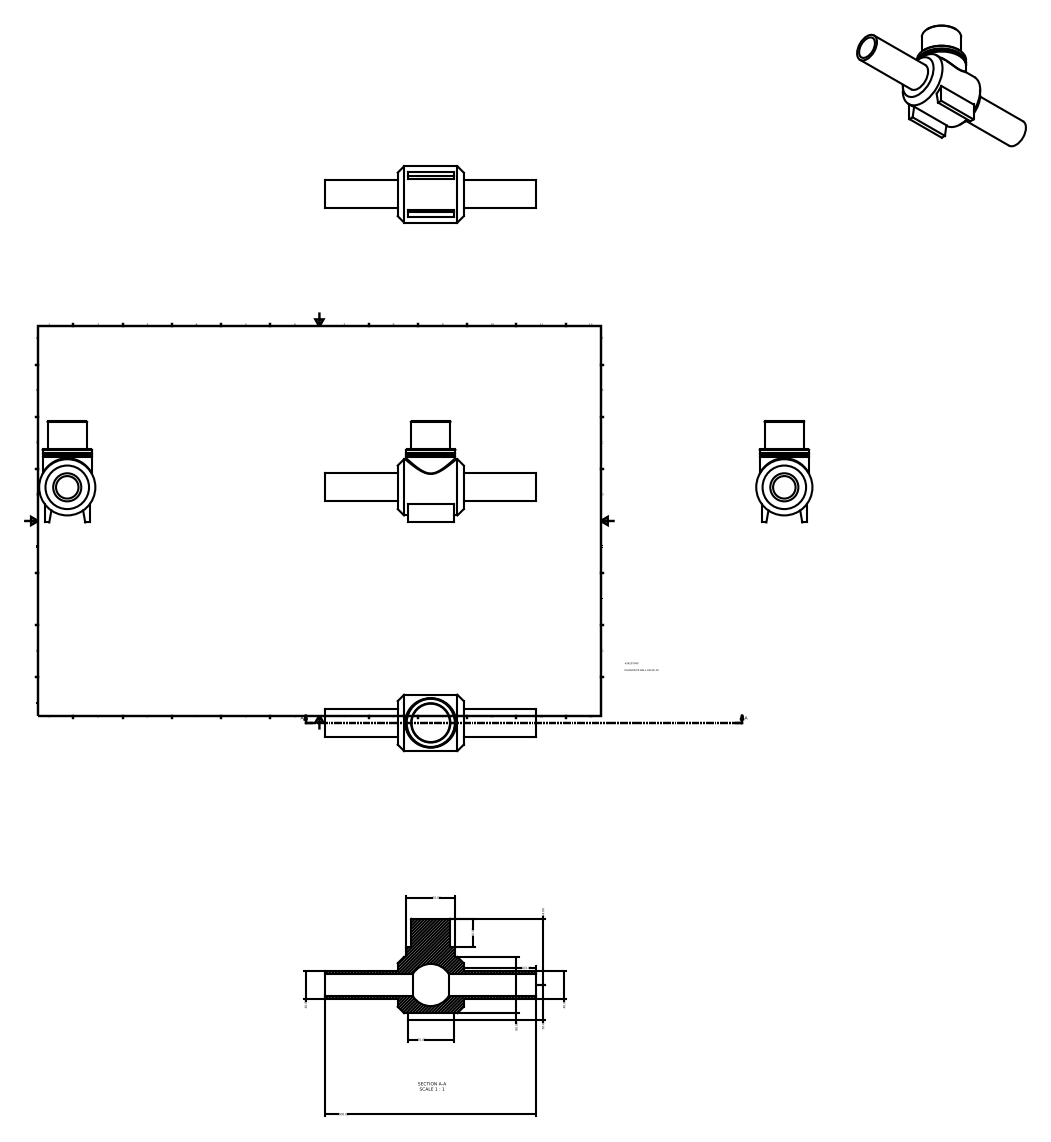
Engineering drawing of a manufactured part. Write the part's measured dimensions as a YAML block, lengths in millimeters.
part_name: "436207040"
step_written_by: "Autodesk Inventor 2015 (AUTOMOTIVE_DESIGN)"
units: millimeters
bodies: {solids: 1, faces: 33, planar: 16, cylindrical: 9, other: 8}
overall_size: [300, 144, 80]
volume: 593829
surface_area: 106908
round_holes:
  - {diameter: 32, count: 1}
round_bosses_or_shafts:
  - {diameter: 80, count: 1}
  - {diameter: 70, count: 1}
  - {diameter: 56, count: 1}
  - {diameter: 40, count: 1}
face_to_face_distances: [94, 64, 40, 103, 197, 104, 144, 117.5, 182.5, 14.5]
